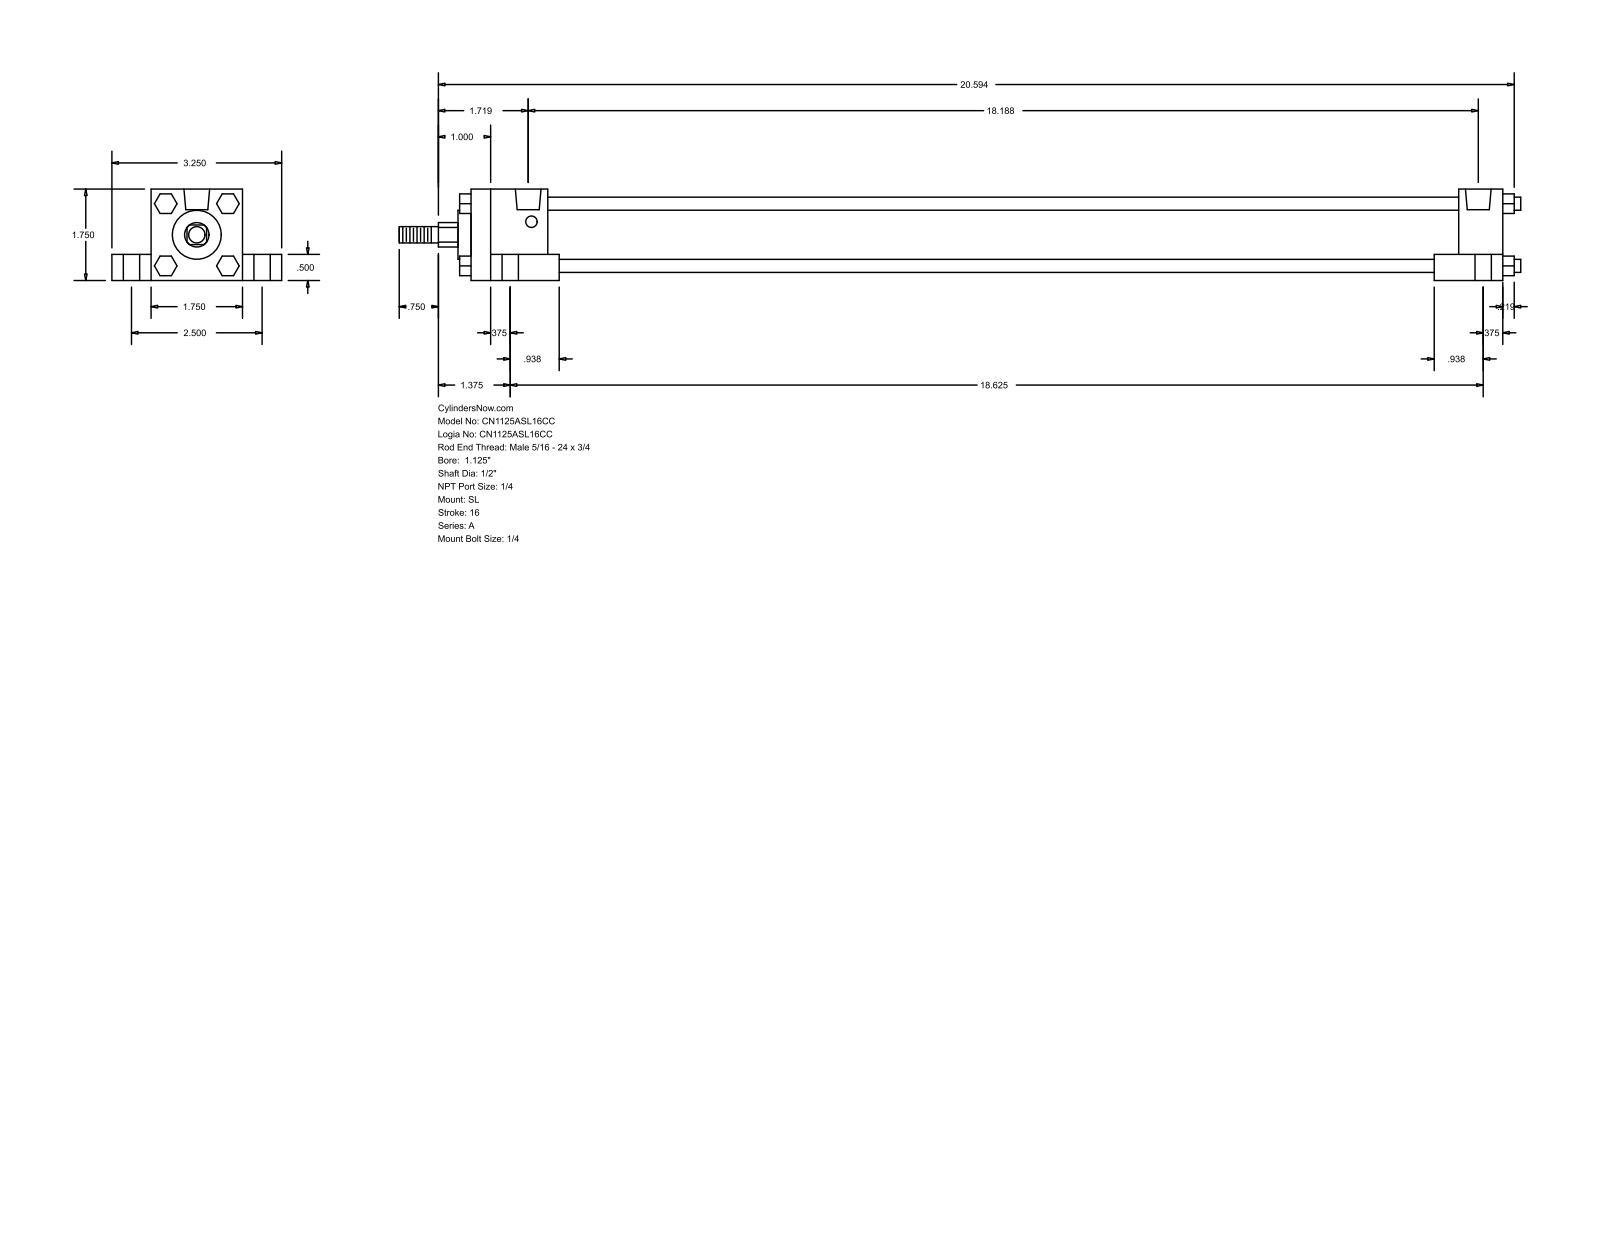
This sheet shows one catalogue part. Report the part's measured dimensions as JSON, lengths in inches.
{"part_name": "A_SL__0112_0.5", "step_written_by": "GSSL Pune (CONFIG_CONTROL_DESIGN)", "units": "inches", "bodies": {"solids": 0, "faces": 150, "planar": 114, "cylindrical": 36, "other": 0}, "overall_size": [21.469, 3.25, 1.75], "round_holes": [[0.219, 4], [0.313, 4], [0.563, 4], [0.492, 2]], "round_bosses_or_shafts": [[0.25, 4], [1.255, 1], [0.937, 1], [0.5, 1], [0.313, 1]], "partial_cylinders_radius": [[0.234, 1]], "face_to_face_distances": [1.75, 1.25, 0.5, 0.75, 2.5, 18.281, 19.75, 18.906, 0.844, 1.469], "hole_center_spacings": [1.254, 1.26, 1.296, 1.315, 2.5, 18.063, 18.262, 18.324]}
